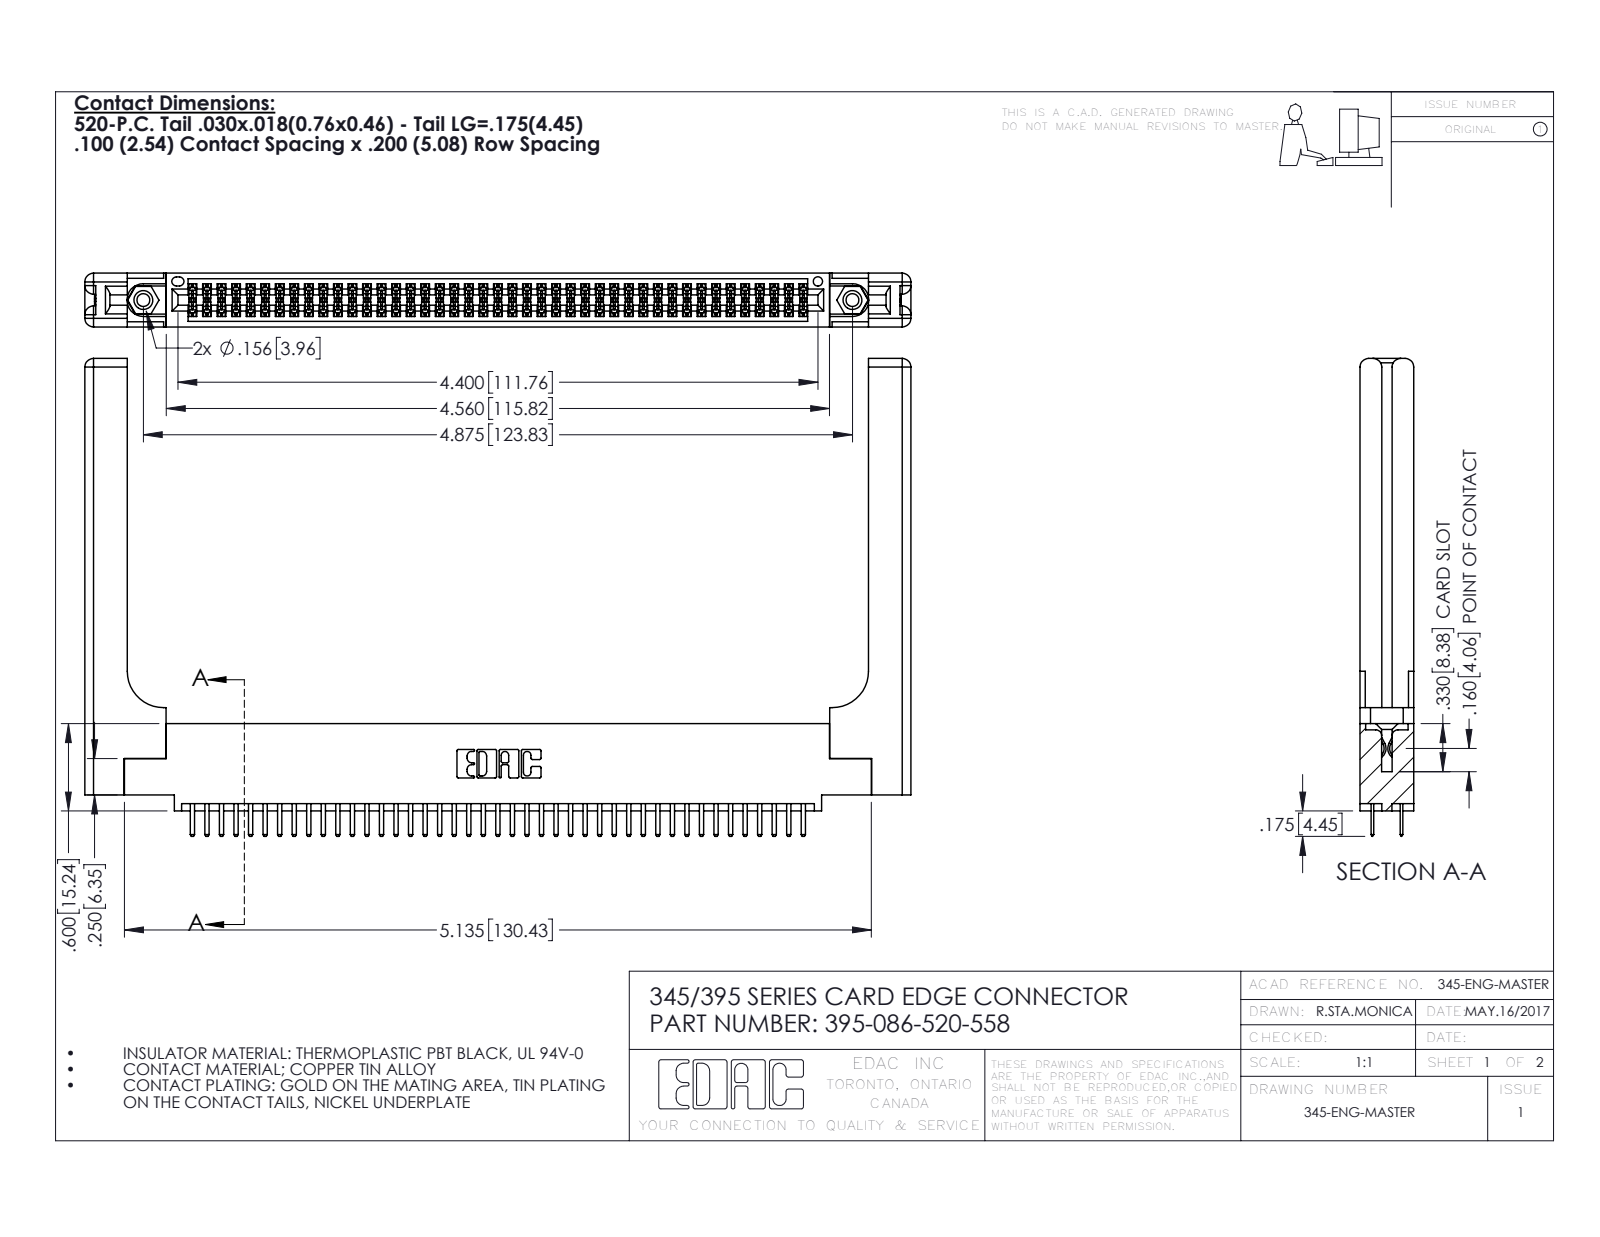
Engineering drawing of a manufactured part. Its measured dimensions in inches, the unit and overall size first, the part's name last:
Units: inches
Overall size (bounding box): 5.679 × 3.285 × 0.37
Round holes (diameter × count): ⌀0.089 ×2, ⌀0.125 ×2, ⌀0.156 ×2, ⌀0.064 ×1
Round bosses / shafts (diameter × count): ⌀0.155 ×2
Partial cylindrical surfaces — rounded edges, fillets, slot ends (radius × count): R0.006 ×129, R0.01 ×90, R0.01 ×22, R0.06 ×16, R0.007 ×6, R0.031 ×6, R0.026 ×3, R0.014 ×2
Main face-to-face distances: 0.072, 0.37, 0.298, 0.2, 0.098, 0.272, 0.025, 0.225, 0.148, 0.15
Hole centre spacings: 0.27, 4.639, 4.875
Volume: 1.366 in³ · Surface area: 39.76 in²
Bodies: 91 solids, 5030 faces (3242 planar, 1728 cylindrical, 60 other)
Part name (STEP PRODUCT): 345-292-001_345-293-120; 345-220-058_345-220-058; 395-086-520-558; 345-250-001_345-250-001-102 (+1 more)
STEP written by: SolidWorks 2016 (CONFIG_CONTROL_DESIGN)
